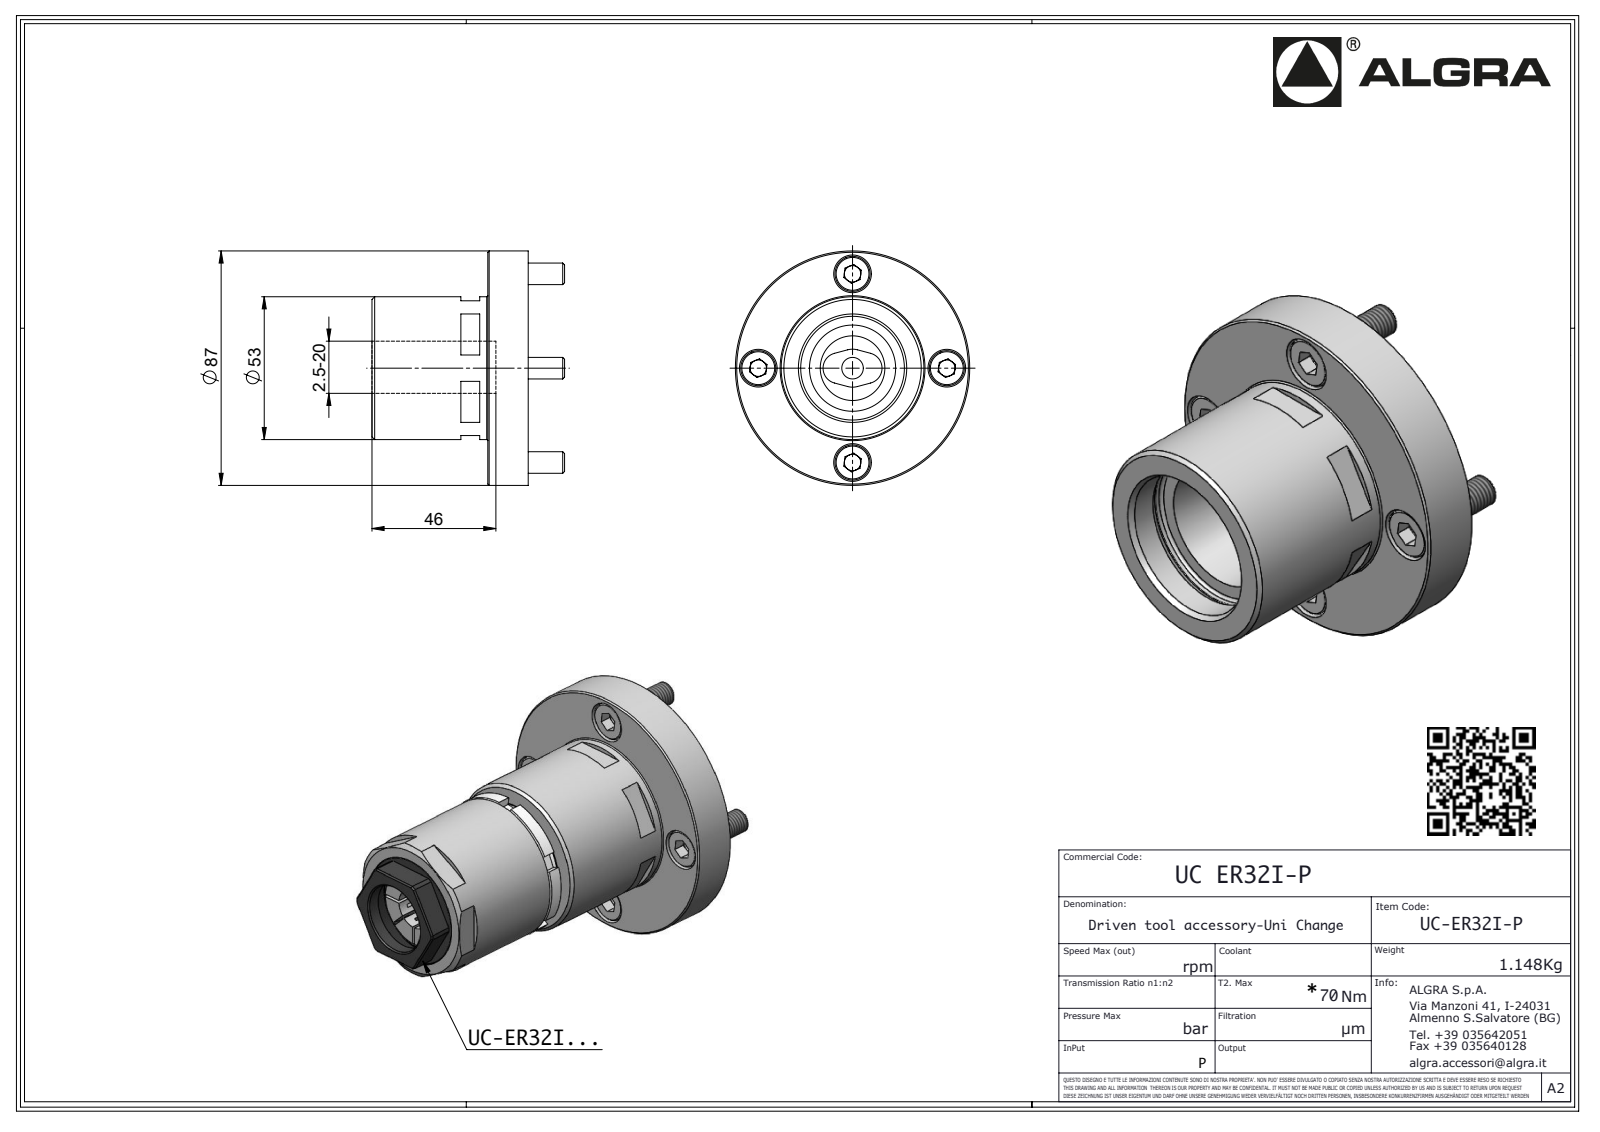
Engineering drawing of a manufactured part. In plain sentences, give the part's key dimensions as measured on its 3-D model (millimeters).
The part is named "UCER32I-P". Its 3-D file was written by "SolidWorks 2016 (AUTOMOTIVE_DESIGN)". It is 1 solid with 270 faces: 179 planar, 32 cylindrical and 59 other. Overall it measures 87 by 87 by 71.5 millimeters. Its volume is 185 863 cubic millimeters and its surface area 24 500 square millimeters. Round holes: 1 of diameter 2.1. Round bosses or shafts: 4 of diameter 8, 1 of diameter 87, 1 of diameter 53, 1 of diameter 6.37, 1 of diameter 1.7. Partial cylindrical surfaces (rounded edges, fillets, slot ends): 7 of radius 0.33, 7 of radius 0.52, 7 of radius 3.7, 1 of radius 0.21. The main face-to-face distances are 15, 58, 43, 50, 13.5, 28.5, 71.5, 31.5, 18, 3.
